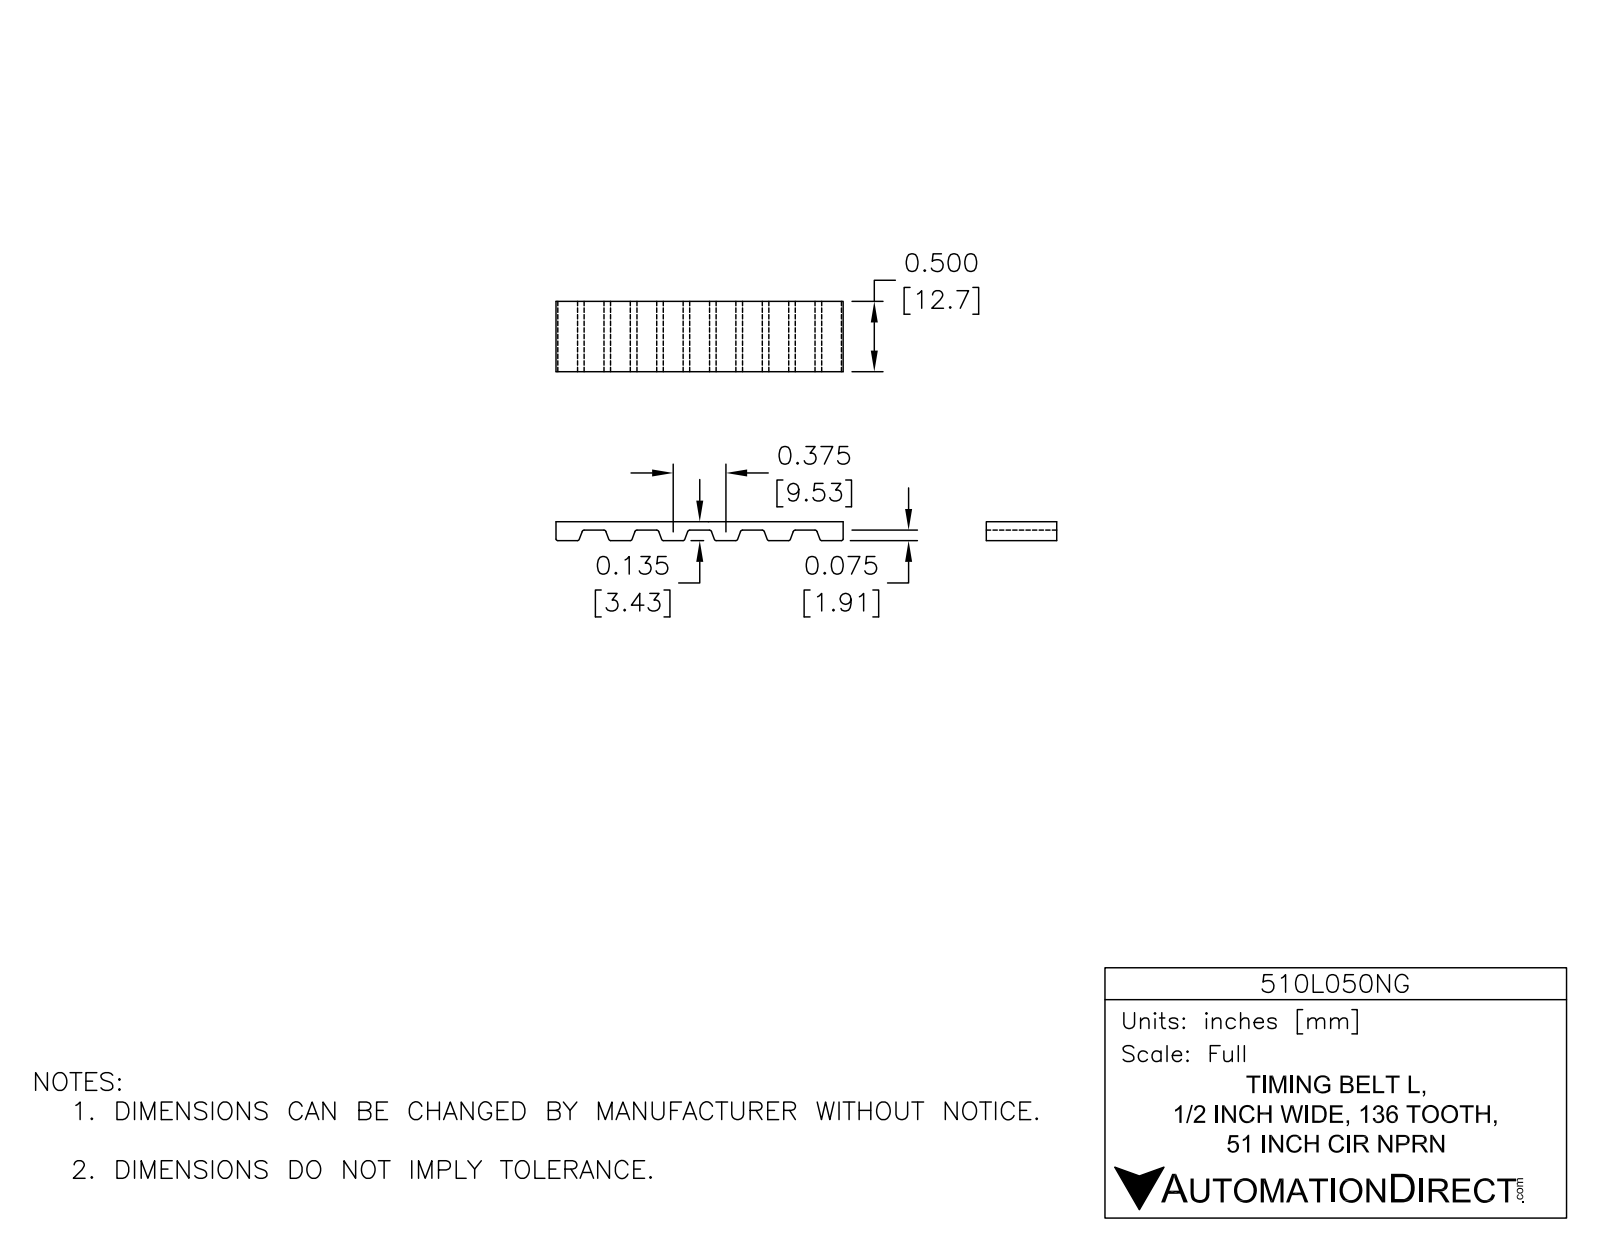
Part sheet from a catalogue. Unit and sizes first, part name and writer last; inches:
Units: inches
Overall size (bounding box): 23.788 × 3 × 0.5
Partial cylindrical surfaces — rounded edges, fillets, slot ends (radius × count): R0.02 ×540, R1.435 ×2, R1.5 ×2
Main face-to-face distances: 0.065, 2.935, 3, 2.87, 0.5, 0.14, 2.86, 0.075, 2.795, 2.72
Volume: 2.316 in³ · Surface area: 66.18 in²
Bodies: 1 solid, 1104 faces (521 planar, 583 cylindrical, 0 other)
Part name (STEP PRODUCT): 510L050NG
STEP written by: SolidWorks 2014 (AUTOMOTIVE_DESIGN)
